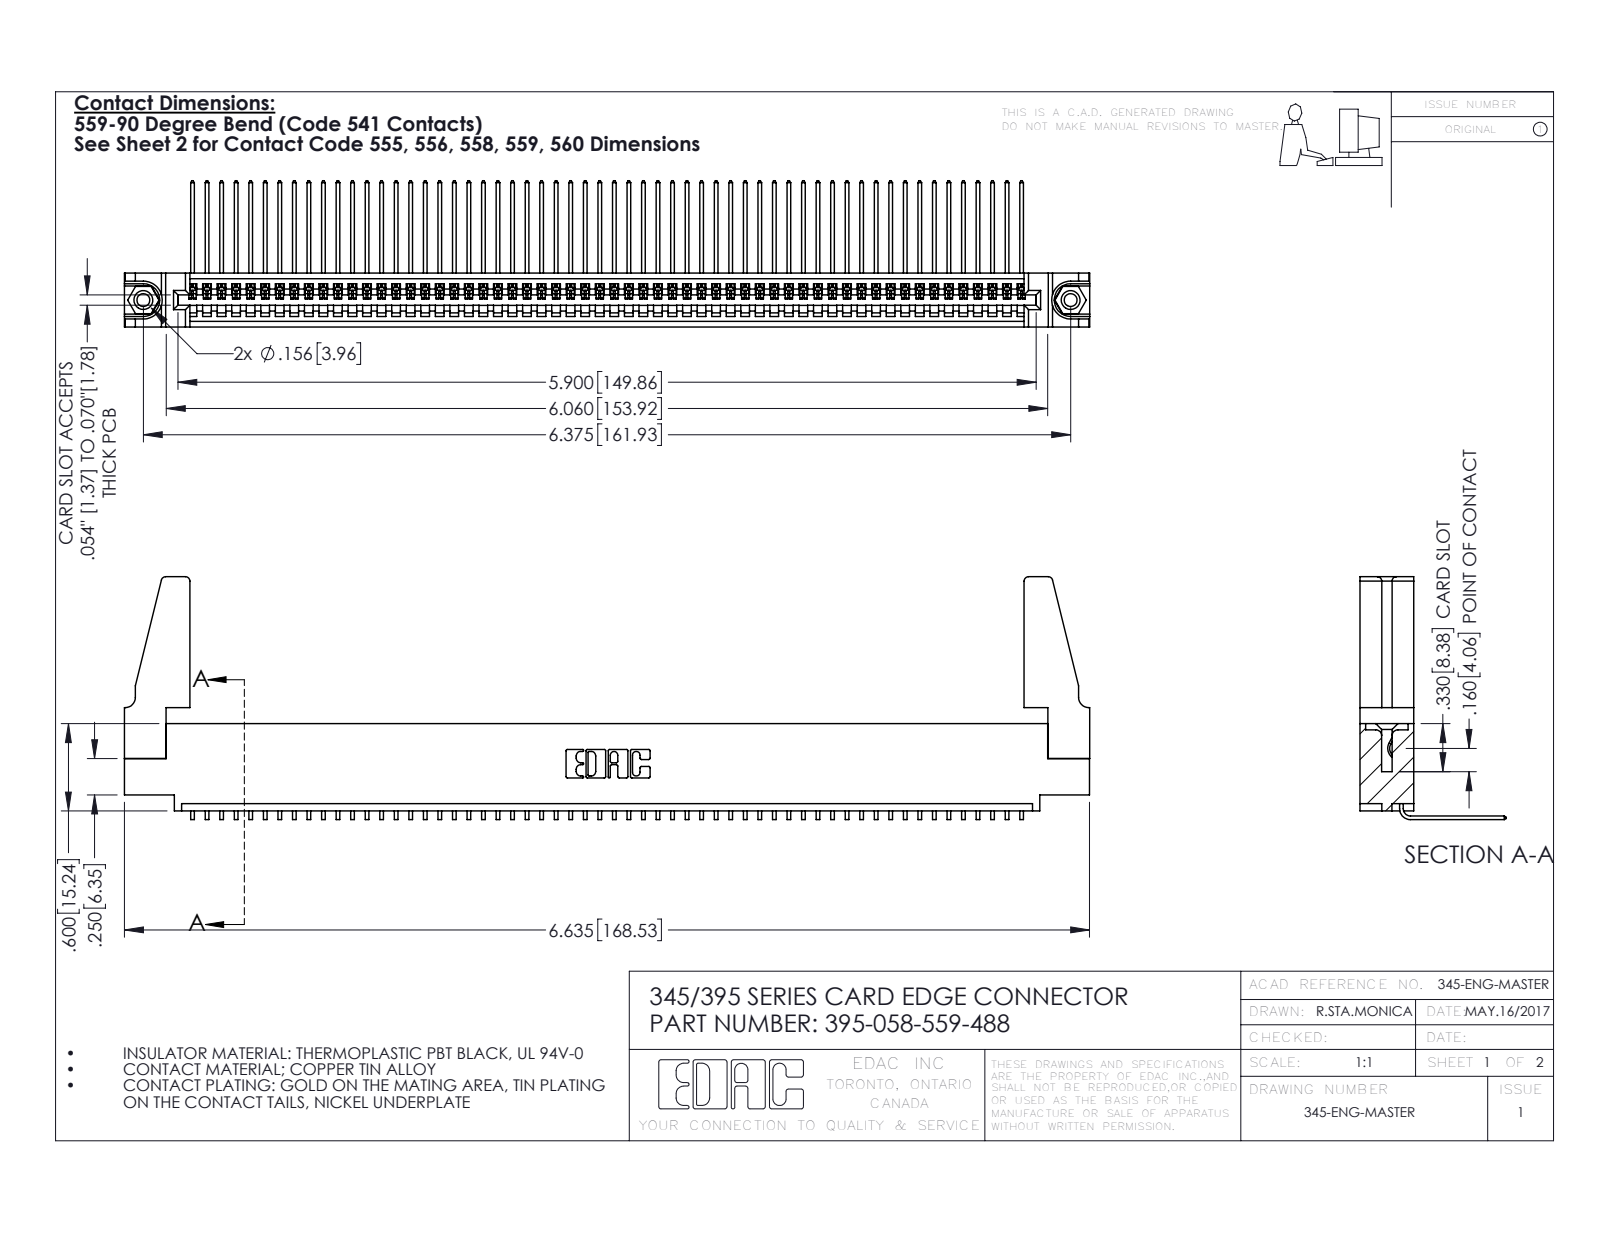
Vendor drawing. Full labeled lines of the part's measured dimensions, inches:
Part name (STEP PRODUCT): 345-220-078_345-220-088; 395-058-559-488; 345 Part_0.110 Offset - 0.156 Dia-TH; 345-250-001_345-250-001-102 (+1 more)
STEP written by: SolidWorks 2016 (CONFIG_CONTROL_DESIGN)
Units: inches
Bodies: 63 solids, 3734 faces (2592 planar, 1126 cylindrical, 16 other)
Overall size (bounding box): 6.636 × 1.669 × 1.005
Volume: 1.191 in³ · Surface area: 40.57 in²
Round holes (diameter × count): ⌀0.089 ×2, ⌀0.125 ×2, ⌀0.156 ×2, ⌀0.064 ×1
Round bosses / shafts (diameter × count): ⌀0.155 ×2
Partial cylindrical surfaces — rounded edges, fillets, slot ends (radius × count): R0.006 ×116, R0.01 ×22, R0.03 ×8, R0.007 ×6, R0.031 ×6, R0.026 ×3, R0.031 ×2, R0.04 ×2
Main face-to-face distances: 0.072, 0.298, 0.37, 0.2, 0.098, 0.272, 0.025, 0.225, 0.149, 0.072
Hole centre spacings: 0.27, 6.139, 6.375
